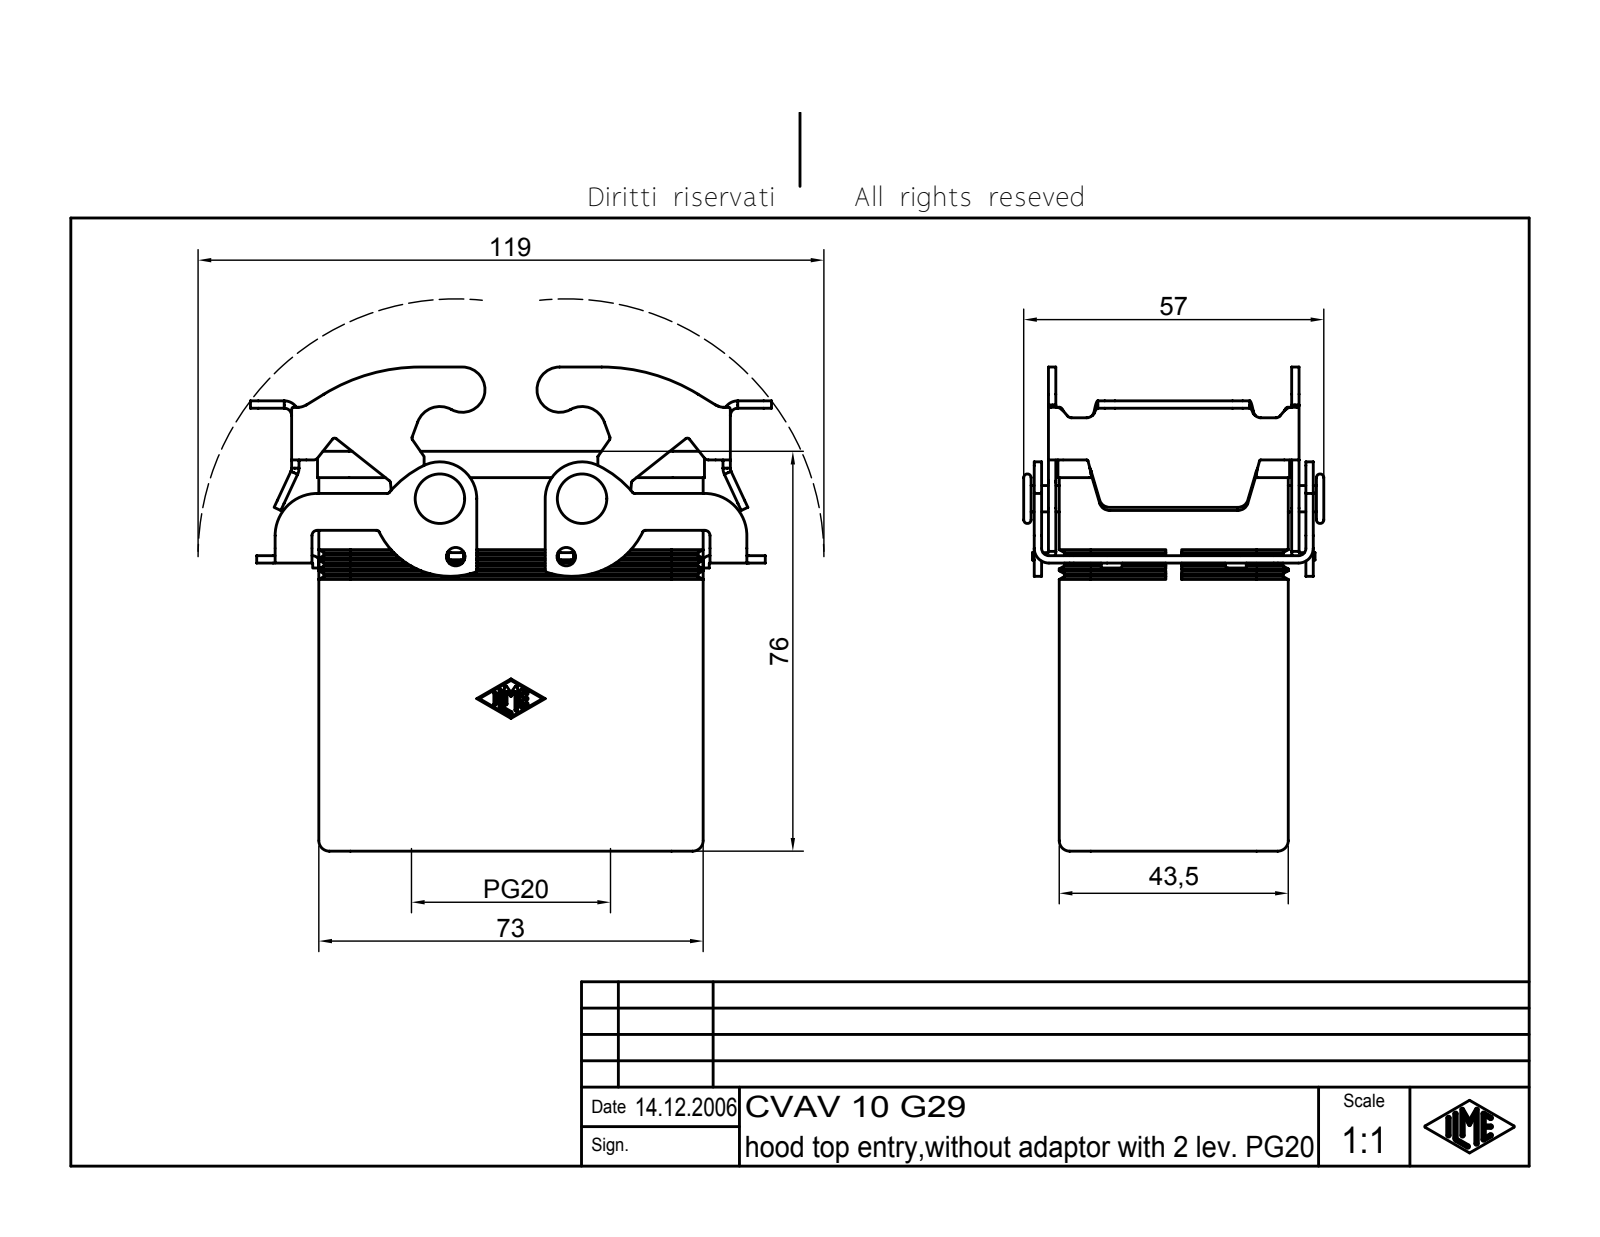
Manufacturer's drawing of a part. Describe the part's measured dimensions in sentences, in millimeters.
The part is named "CVAV 10 G29". Its 3-D file was written by "Autodesk Inventor 7 (AUTOMOTIVE_DESIGN)". It is 3 solids with 706 faces: 205 planar, 182 cylindrical and 319 other. Overall it measures 98.97 by 91.91 by 57 millimeters. Its volume is 80 970 cubic millimeters and its surface area 54 704 square millimeters. Round holes: 2 of diameter 3.5, 1 of diameter 35.48. Round bosses or shafts: 2 of diameter 5, 2 of diameter 3.2. Partial cylindrical surfaces (rounded edges, fillets, slot ends): 18 of radius 0.5, 16 of radius 0.25, 14 of radius 1, 12 of radius 1.5, 12 of radius 2, 10 of radius 1.4, 10 of radius 2.8, 8 of radius 6. The main face-to-face distances are 3, 40.5, 43.5, 37.5, 1.4, 70, 8.5, 73, 11.75, 2.7. The hole center spacings are 21.
